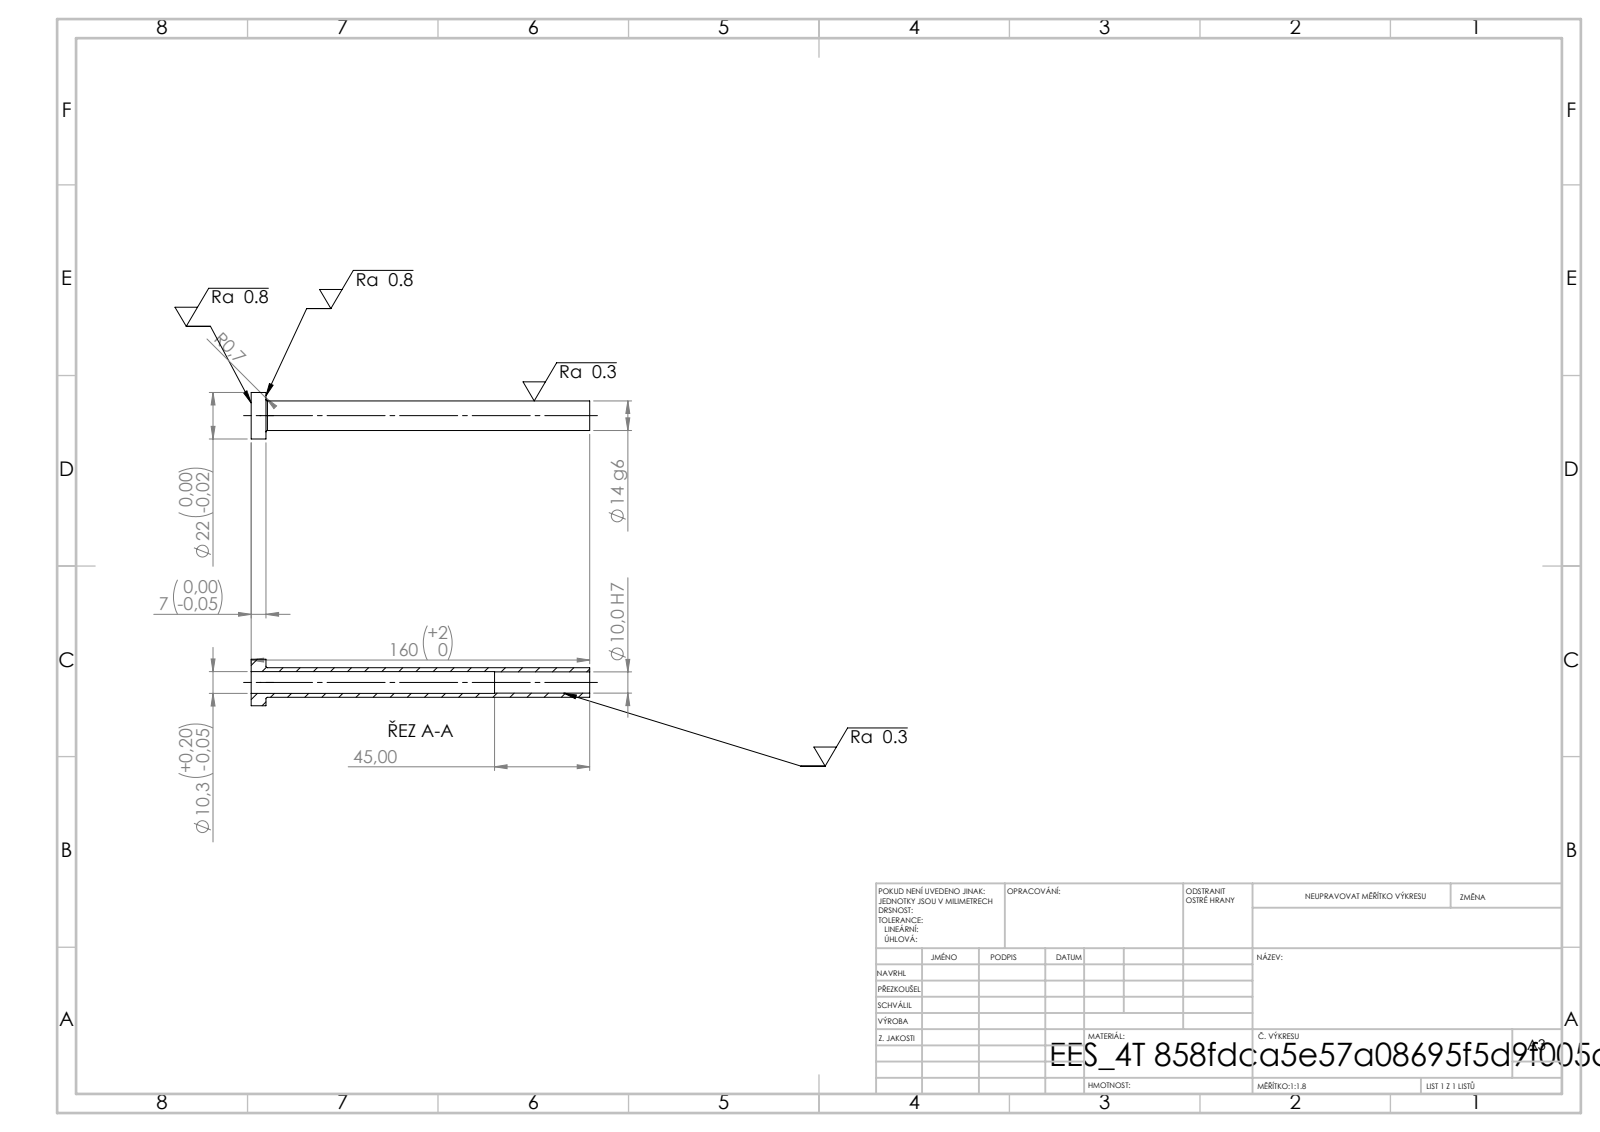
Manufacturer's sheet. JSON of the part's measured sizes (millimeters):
{"step_written_by": "SolidWorks 2019 (CONFIG_CONTROL_DESIGN)", "units": "millimeters", "bodies": {"solids": 1, "faces": 14, "planar": 4, "cylindrical": 8, "other": 2}, "overall_size": [160, 22, 22], "volume_mm3": 13102, "surface_area_mm2": 12938, "round_holes": [[10, 1], [10.3, 1]], "round_bosses_or_shafts": [[22, 1], [14, 1]], "face_to_face_distances": [7, 160, 153, 115, 108, 45]}
